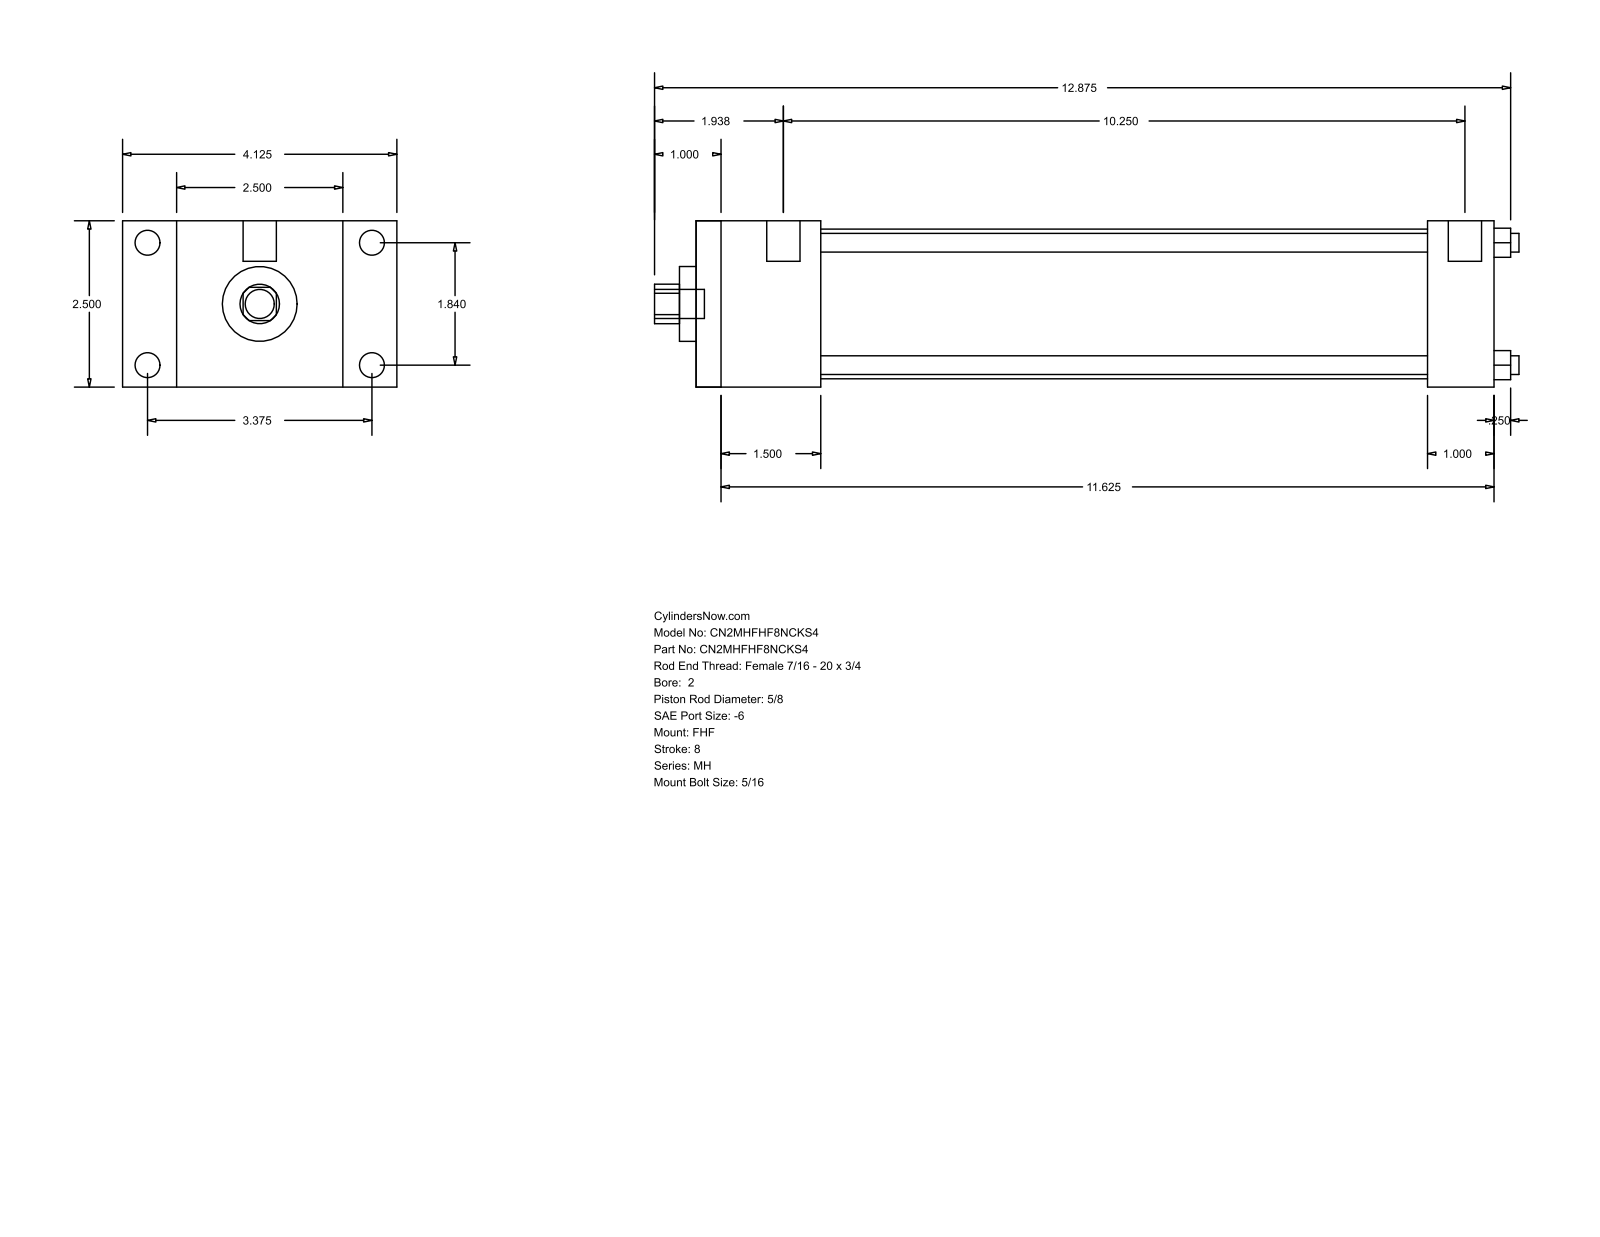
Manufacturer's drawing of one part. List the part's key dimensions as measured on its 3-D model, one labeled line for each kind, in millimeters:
Part name (STEP PRODUCT): MH_FHF__0200_0.625
STEP written by: GSSL Pune (CONFIG_CONTROL_DESIGN)
Units: millimetres
Bodies: 0 solids, 88 faces (60 planar, 28 cylindrical, 0 other)
Overall size (bounding box): 330.2 × 104.78 × 63.5
Round holes (diameter × count): ⌀7.14 ×4, ⌀15.88 ×1, ⌀28.57 ×1, ⌀57.15 ×1
Round bosses / shafts (diameter × count): ⌀9.53 ×4, ⌀5.56 ×4, ⌀12.7 ×2, ⌀11.11 ×1
Partial cylindrical surfaces — rounded edges, fillets, slot ends (radius × count): R7.54 ×1
Main face-to-face distances: 63.5, 47.62, 304.8, 257.18, 20.64, 84.14, 104.78, 279.39, 231.77, 25.41
Hole centre spacings: 33.05, 46.74, 66.1
